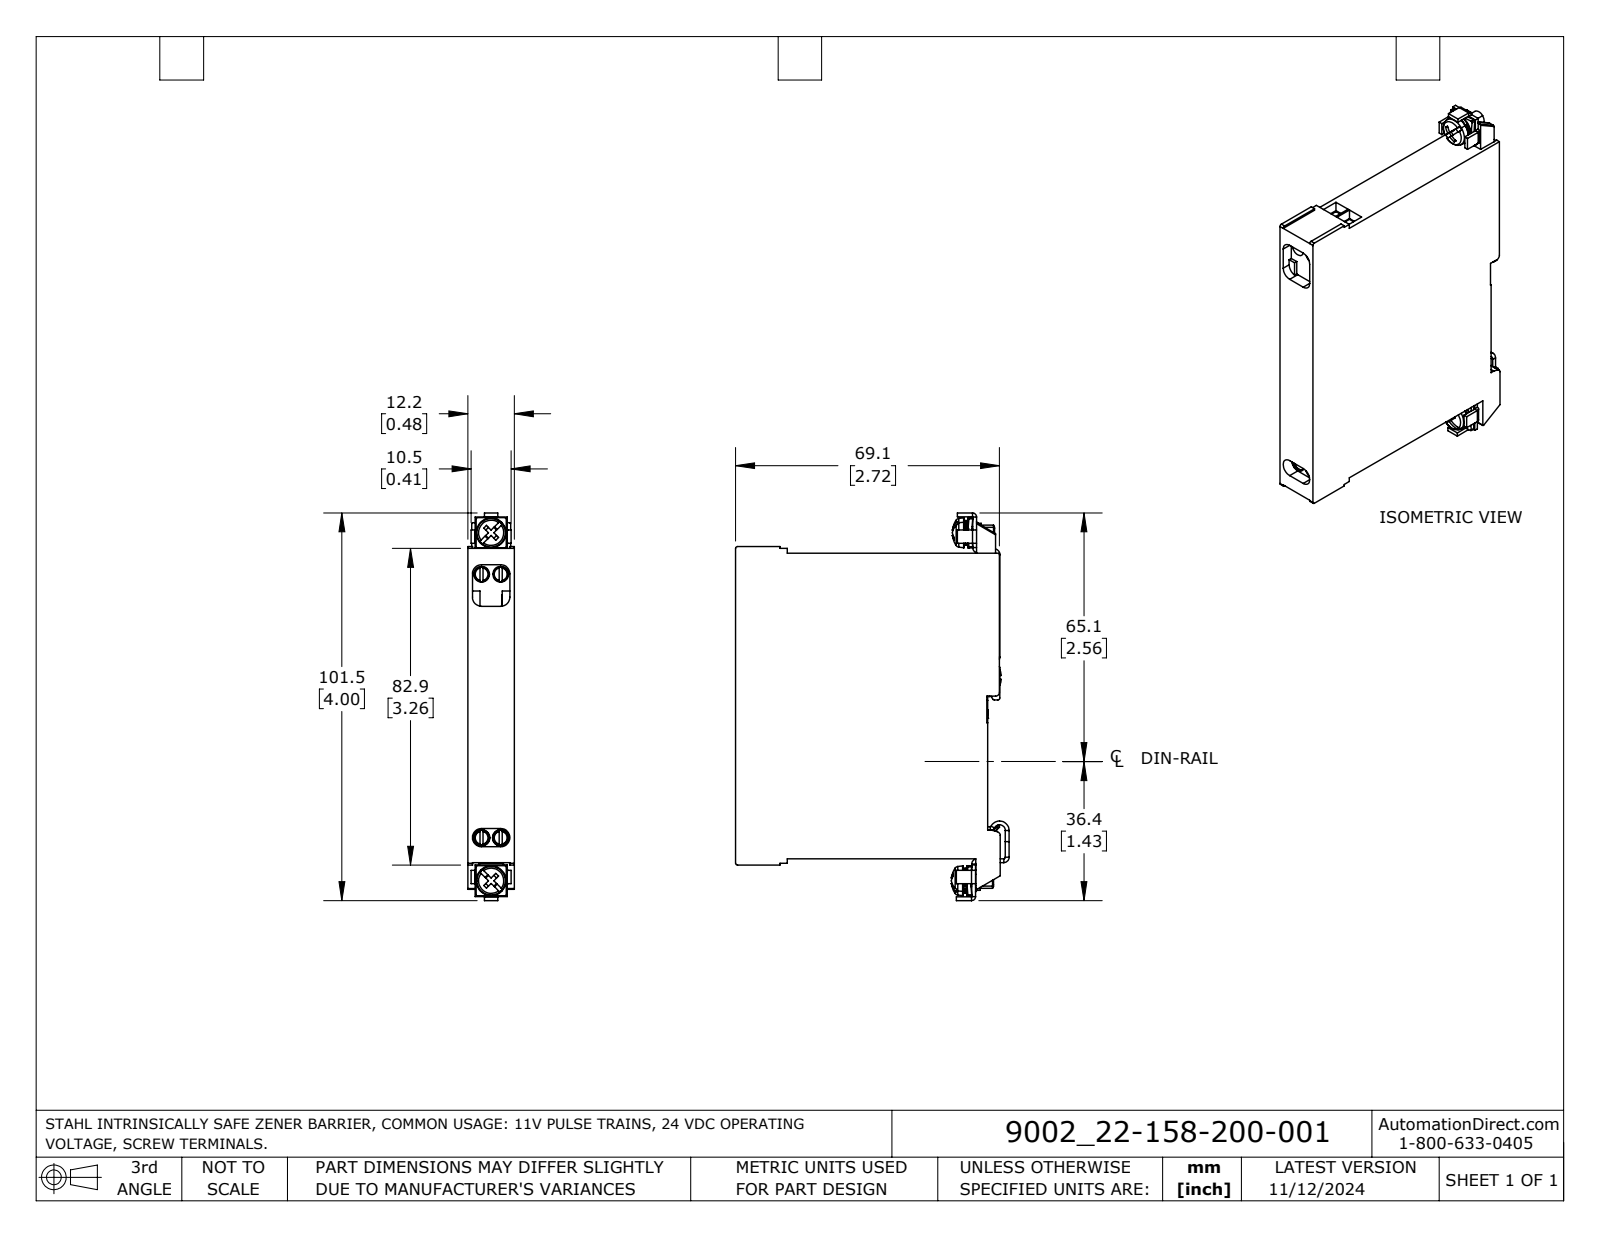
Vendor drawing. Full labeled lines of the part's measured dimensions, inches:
Part name (STEP PRODUCT): 900222-158-200-001
STEP written by: SolidWorks 2023 (AUTOMOTIVE_DESIGN)
Units: inches
Bodies: 4 solids, 762 faces (528 planar, 146 cylindrical, 88 other)
Overall size (bounding box): 3.996 × 2.82 × 0.48
Volume: 3.982 in³ · Surface area: 33.72 in²
Round holes (diameter × count): ⌀0.161 ×4, ⌀0.169 ×3, ⌀0.128 ×2, ⌀0.165 ×2, ⌀0.118 ×1
Round bosses / shafts (diameter × count): ⌀0.307 ×3, ⌀0.157 ×3, ⌀0.197 ×2, ⌀0.124 ×2, ⌀0.256 ×1
Partial cylindrical surfaces — rounded edges, fillets, slot ends (radius × count): R0.02 ×16, R0.012 ×8, R0.016 ×6, R0.039 ×6, R0.041 ×6, R0.055 ×6, R0.094 ×6, R0.01 ×4
Main face-to-face distances: 0.48, 0.039, 3.11, 0.043, 0.079, 3.071, 0.087, 3.15, 0.083, 0.047
Hole centre spacings: 0.197, 0.438, 0.454, 1.068, 1.111, 1.613, 1.656, 2.717
